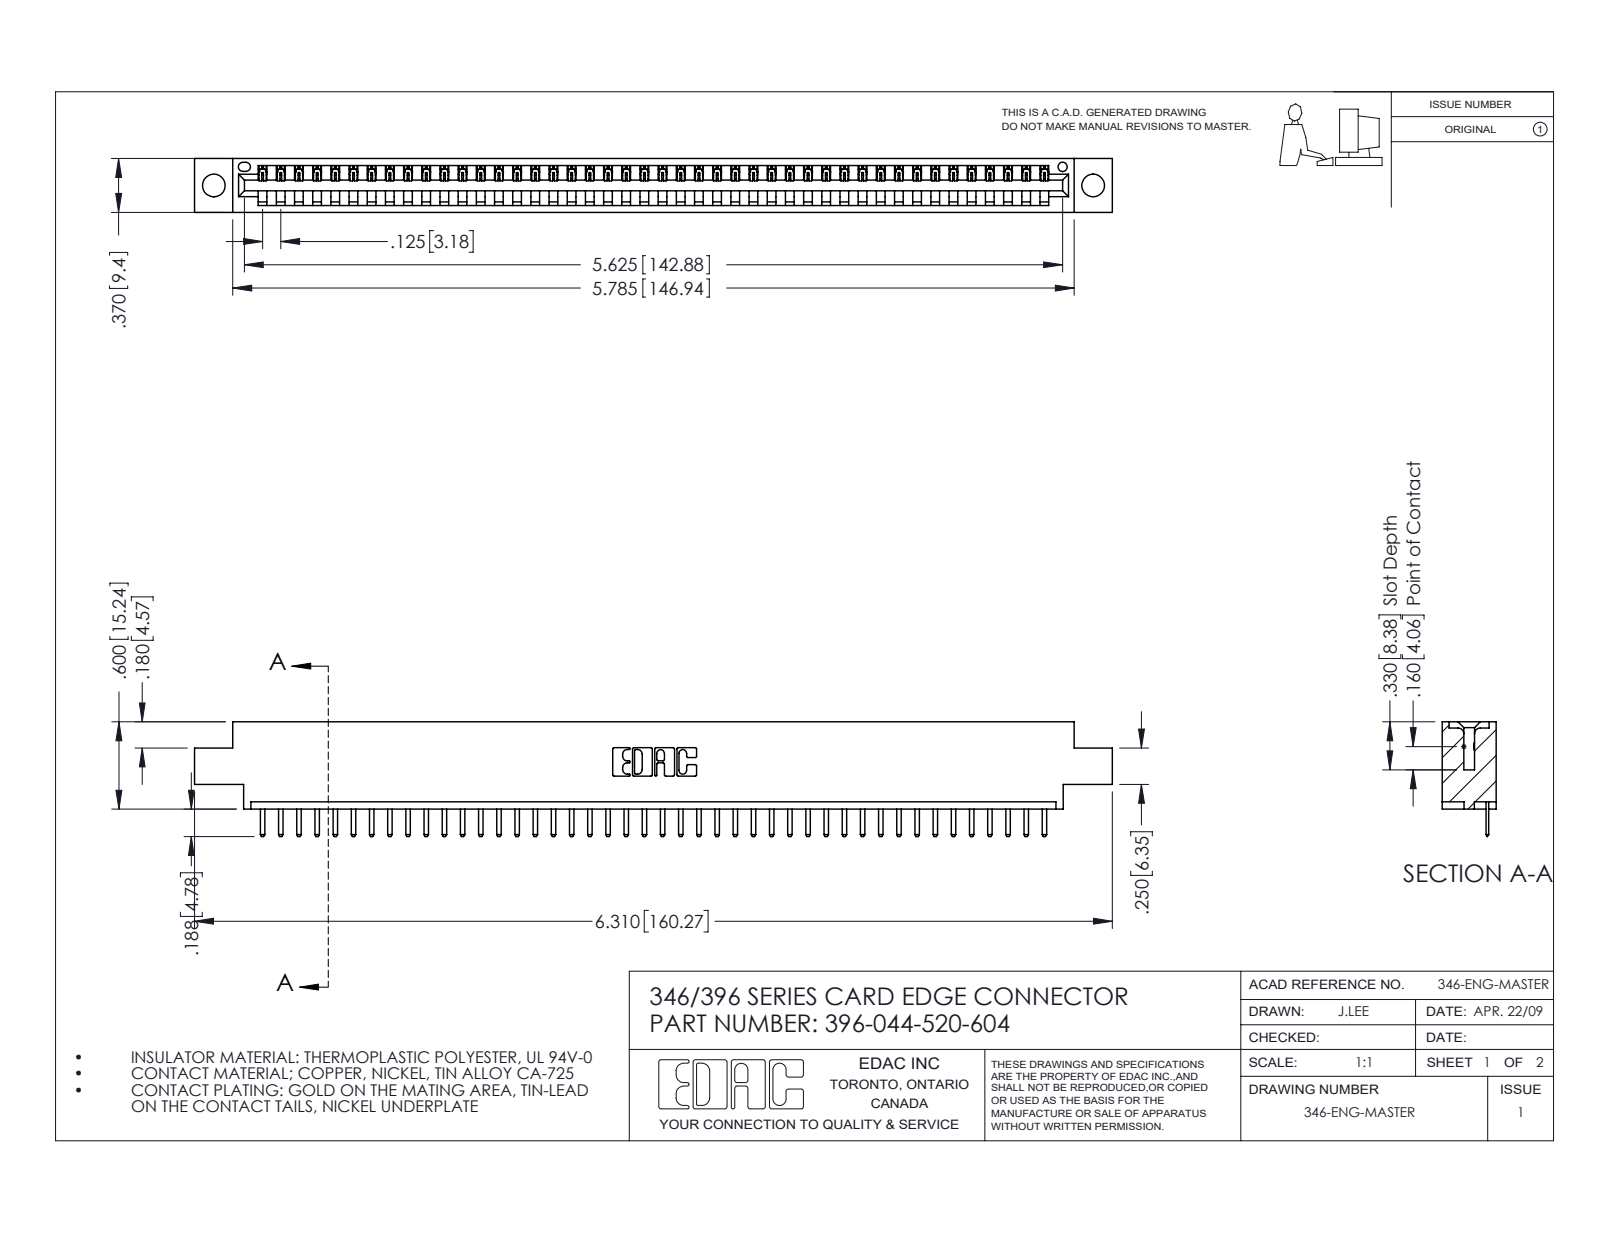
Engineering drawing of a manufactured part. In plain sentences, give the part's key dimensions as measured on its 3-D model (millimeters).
The part is named "396-044-520-604; 345-292-001_345-293-120; 346 Part_0.170 Offset - 0.156 Dia-TH". Its 3-D file was written by "SolidWorks 2016 (CONFIG_CONTROL_DESIGN)". It is 45 solids with 2854 faces: 1928 planar, 926 cylindrical and 0 other. Overall it measures 160.3 by 20 by 9.4 millimeters. Its volume is 15 000 cubic millimeters and its surface area 18 300 square millimeters. Round holes: 2 of diameter 4, 1 of diameter 1.6. Partial cylindrical surfaces (rounded edges, fillets, slot ends): 90 of radius 0.3, 88 of radius 0.2, 22 of radius 0.3, 6 of radius 0.2, 6 of radius 0.8, 3 of radius 0.7, 2 of radius 0.8, 2 of radius 1. The main face-to-face distances are 1.2, 8.2, 9.4, 6.4, 3.8, 5.6, 2.5, 4.4, 1.8, 7.6. The hole center spacings are 6.2, 148.2, 153.5.
